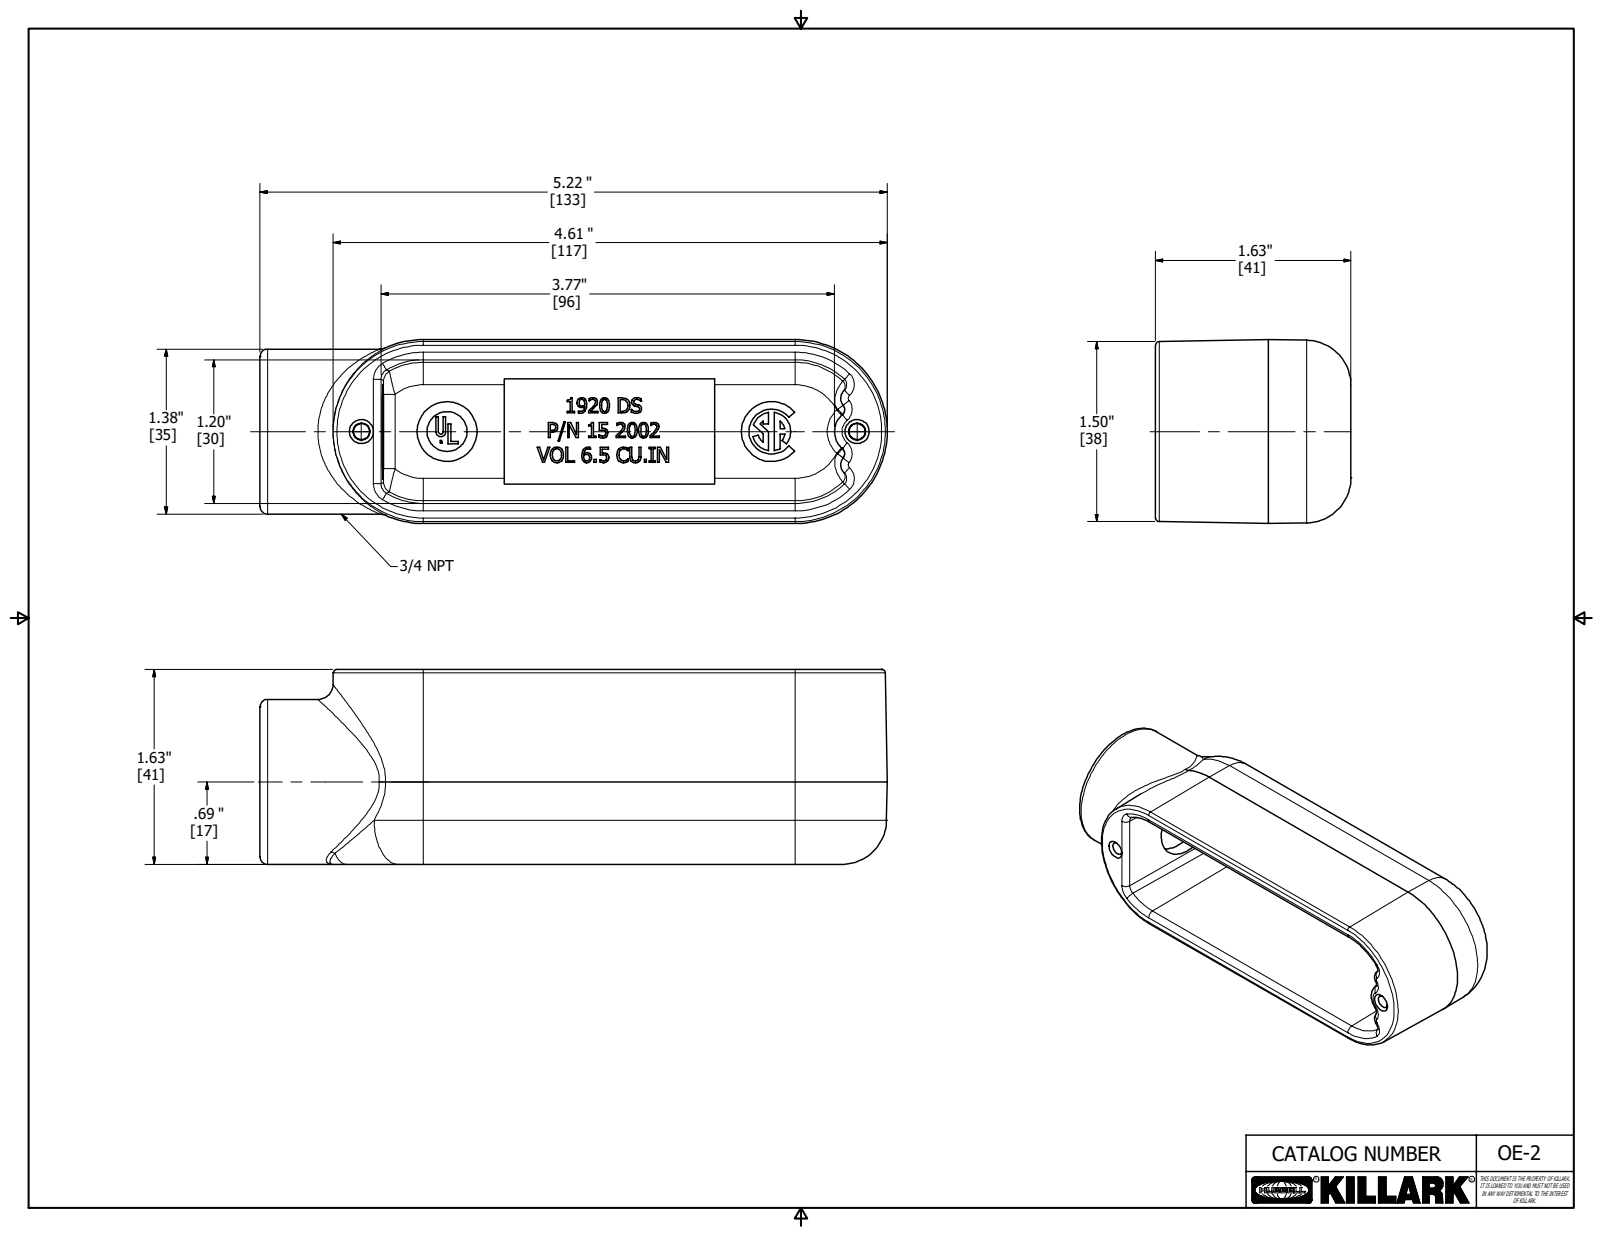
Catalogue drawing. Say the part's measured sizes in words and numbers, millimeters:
The part is named "13749-1". Its 3-D file was written by "Autodesk Inventor 2018 (AUTOMOTIVE_DESIGN)". It is 1 solid with 836 faces: 459 planar, 33 cylindrical and 344 other. Overall it measures 132.6 by 41.3 by 38.9 millimeters. Its volume is 68 040 cubic millimeters and its surface area 30 810 square millimeters. Round holes: 1 of diameter 8.4, 1 of diameter 20.1. Round bosses or shafts: 1 of diameter 34.9, 1 of diameter 12.6. Partial cylindrical surfaces (rounded edges, fillets, slot ends): 4 of radius 4.7, 3 of radius 1.6, 3 of radius 2.4, 2 of radius 0.8, 2 of radius 1.5, 2 of radius 9.5, 1 of radius 0.2, 1 of radius 0.5. The main face-to-face distances are 34.3, 4.6, 38.9, 4.2, 3.8, 0.4, 0.4, 41.3, 37.5, 37.1.
